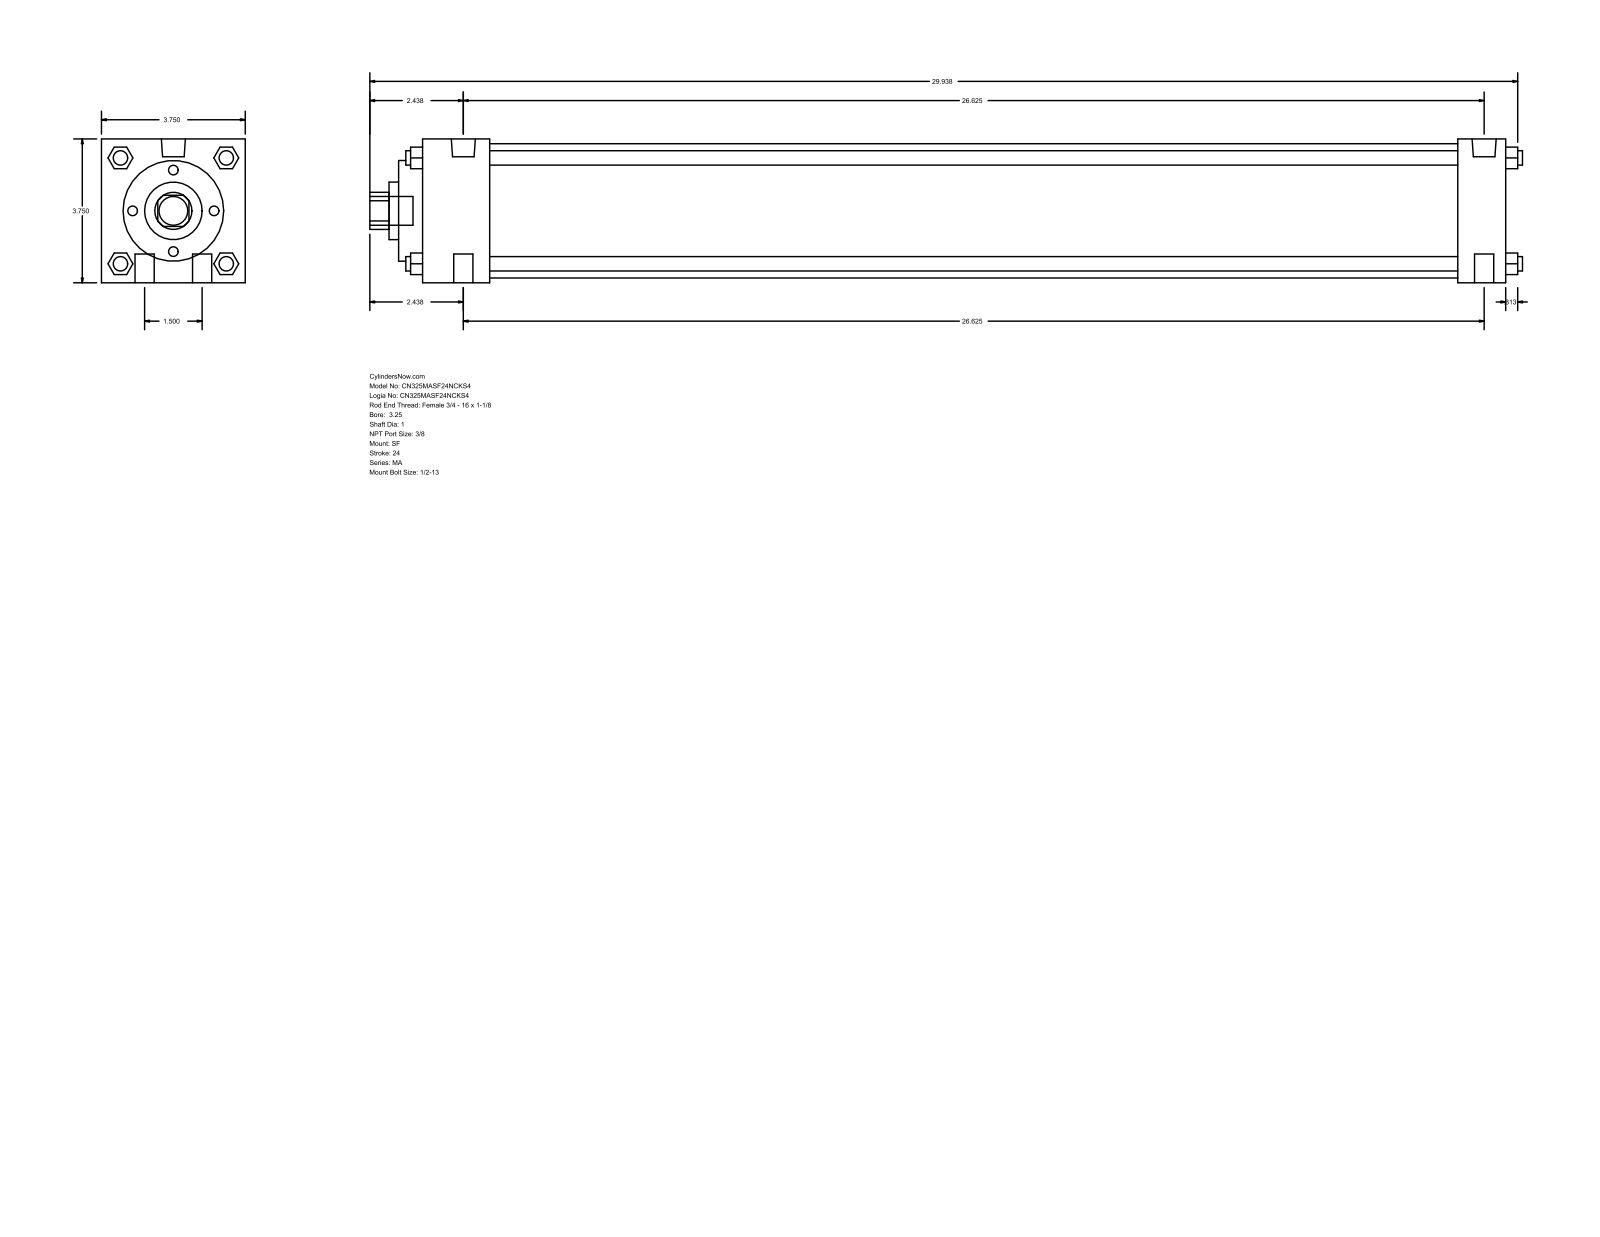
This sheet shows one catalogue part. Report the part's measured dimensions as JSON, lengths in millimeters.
{"part_name": "MA_SF__0325_1", "step_written_by": "GSSL Pune (CONFIG_CONTROL_DESIGN)", "units": "millimeters", "bodies": {"solids": 0, "faces": 126, "planar": 95, "cylindrical": 31, "other": 0}, "overall_size": [763.59, 95.25, 95.25], "round_holes": [[25.4, 1], [38.1, 1], [66.67, 1], [88.9, 1]], "round_bosses_or_shafts": [[12.7, 4], [9.53, 4], [15.93, 2], [11.11, 2], [19.05, 1]], "partial_cylinders_radius": [[12.29, 1]], "face_to_face_distances": [95.24, 717.56, 15.87, 685.81, 31.75, 44.46, 641.35, 673.1, 60.33, 701.68]}
